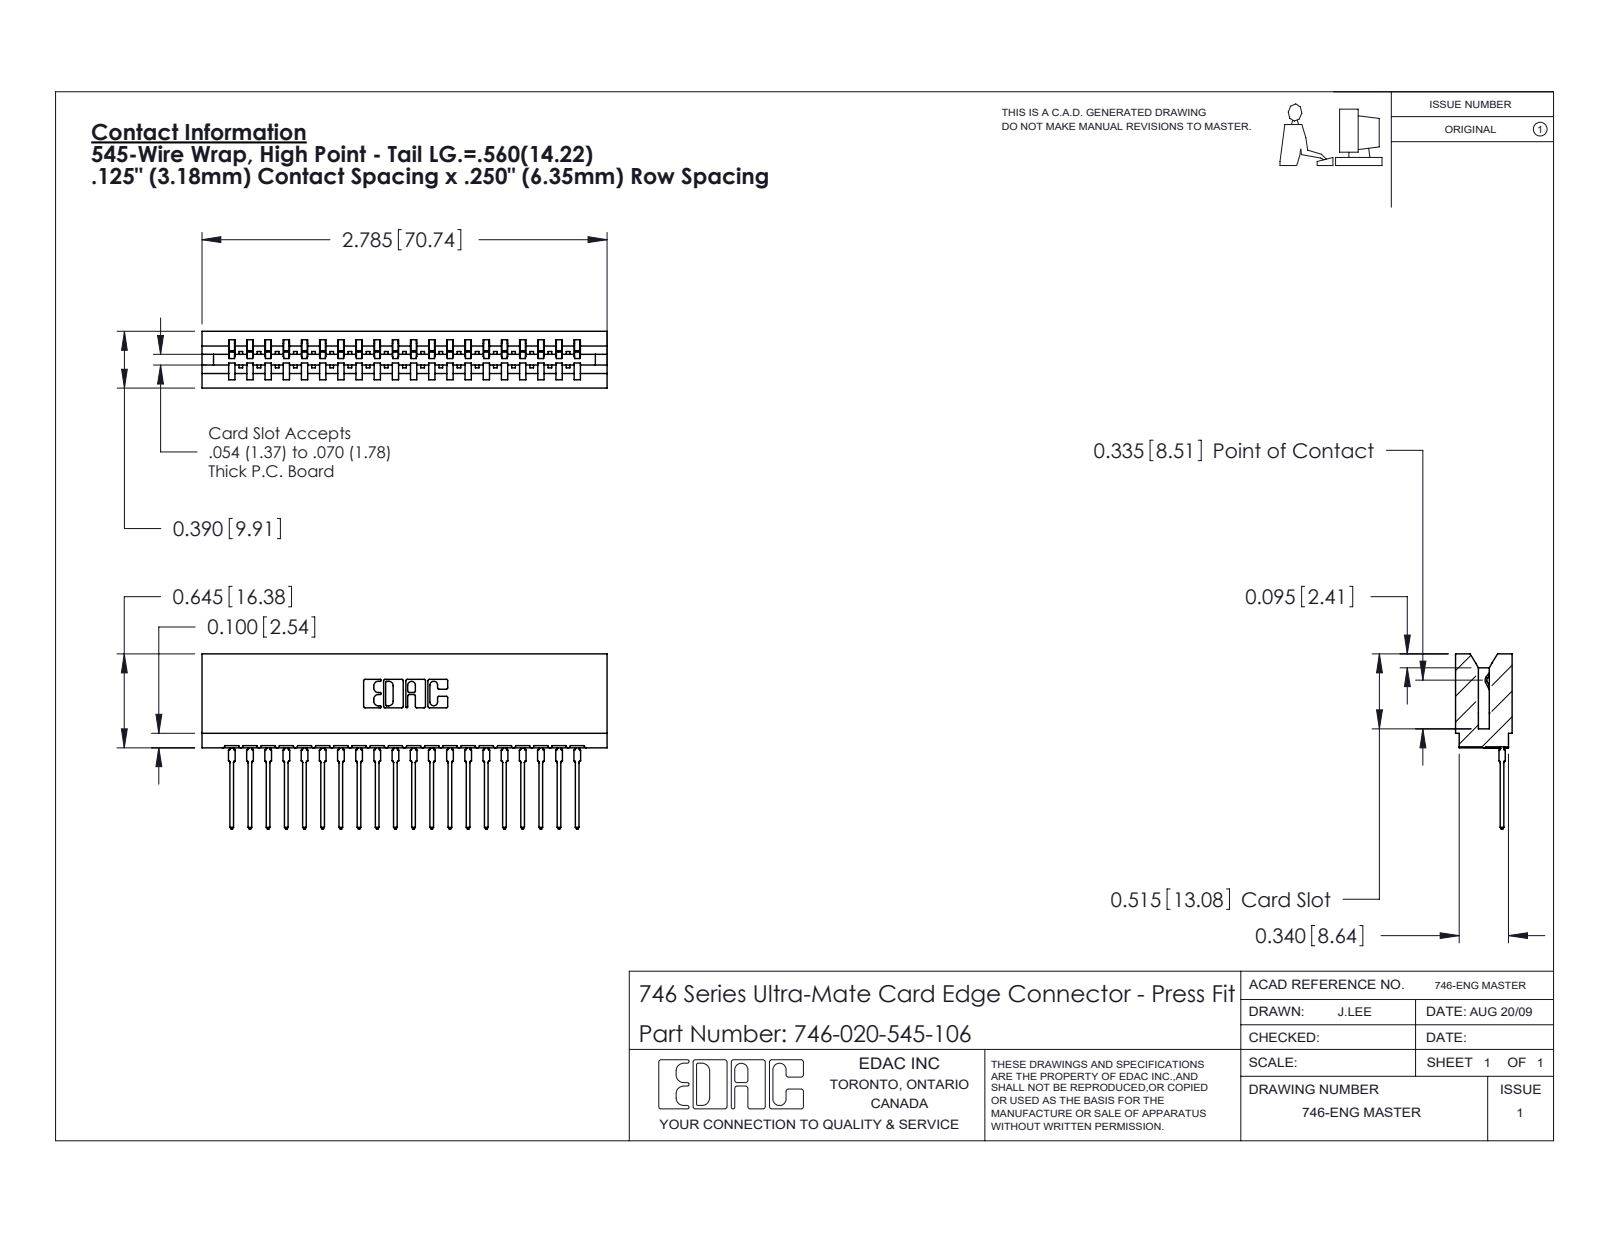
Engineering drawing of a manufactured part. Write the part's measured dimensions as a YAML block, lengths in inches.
part_name: "746 Part_.515 Slot Depth - 06; 746-292-001_545; 746-020-545-106"
step_written_by: "SolidWorks 2020 (CONFIG_CONTROL_DESIGN)"
units: inches
bodies: {solids: 21, faces: 2258, planar: 1316, cylindrical: 422, other: 520}
overall_size: [2.785, 1.204, 0.39]
volume: 0.462
surface_area: 17.29
partial_cylinders:
  - {radius: 0.021, count: 40}
  - {radius: 0.01, count: 22}
  - {radius: 0.015, count: 21}
  - {radius: 0.007, count: 6}
  - {radius: 0.031, count: 6}
  - {radius: 0.005, count: 4}
  - {radius: 0.011, count: 4}
  - {radius: 0.026, count: 3}
face_to_face_distances: [0.25, 0.333, 0.057, 0.39, 0.5, 0.025, 0.307, 0.083, 0.125, 0.375]
